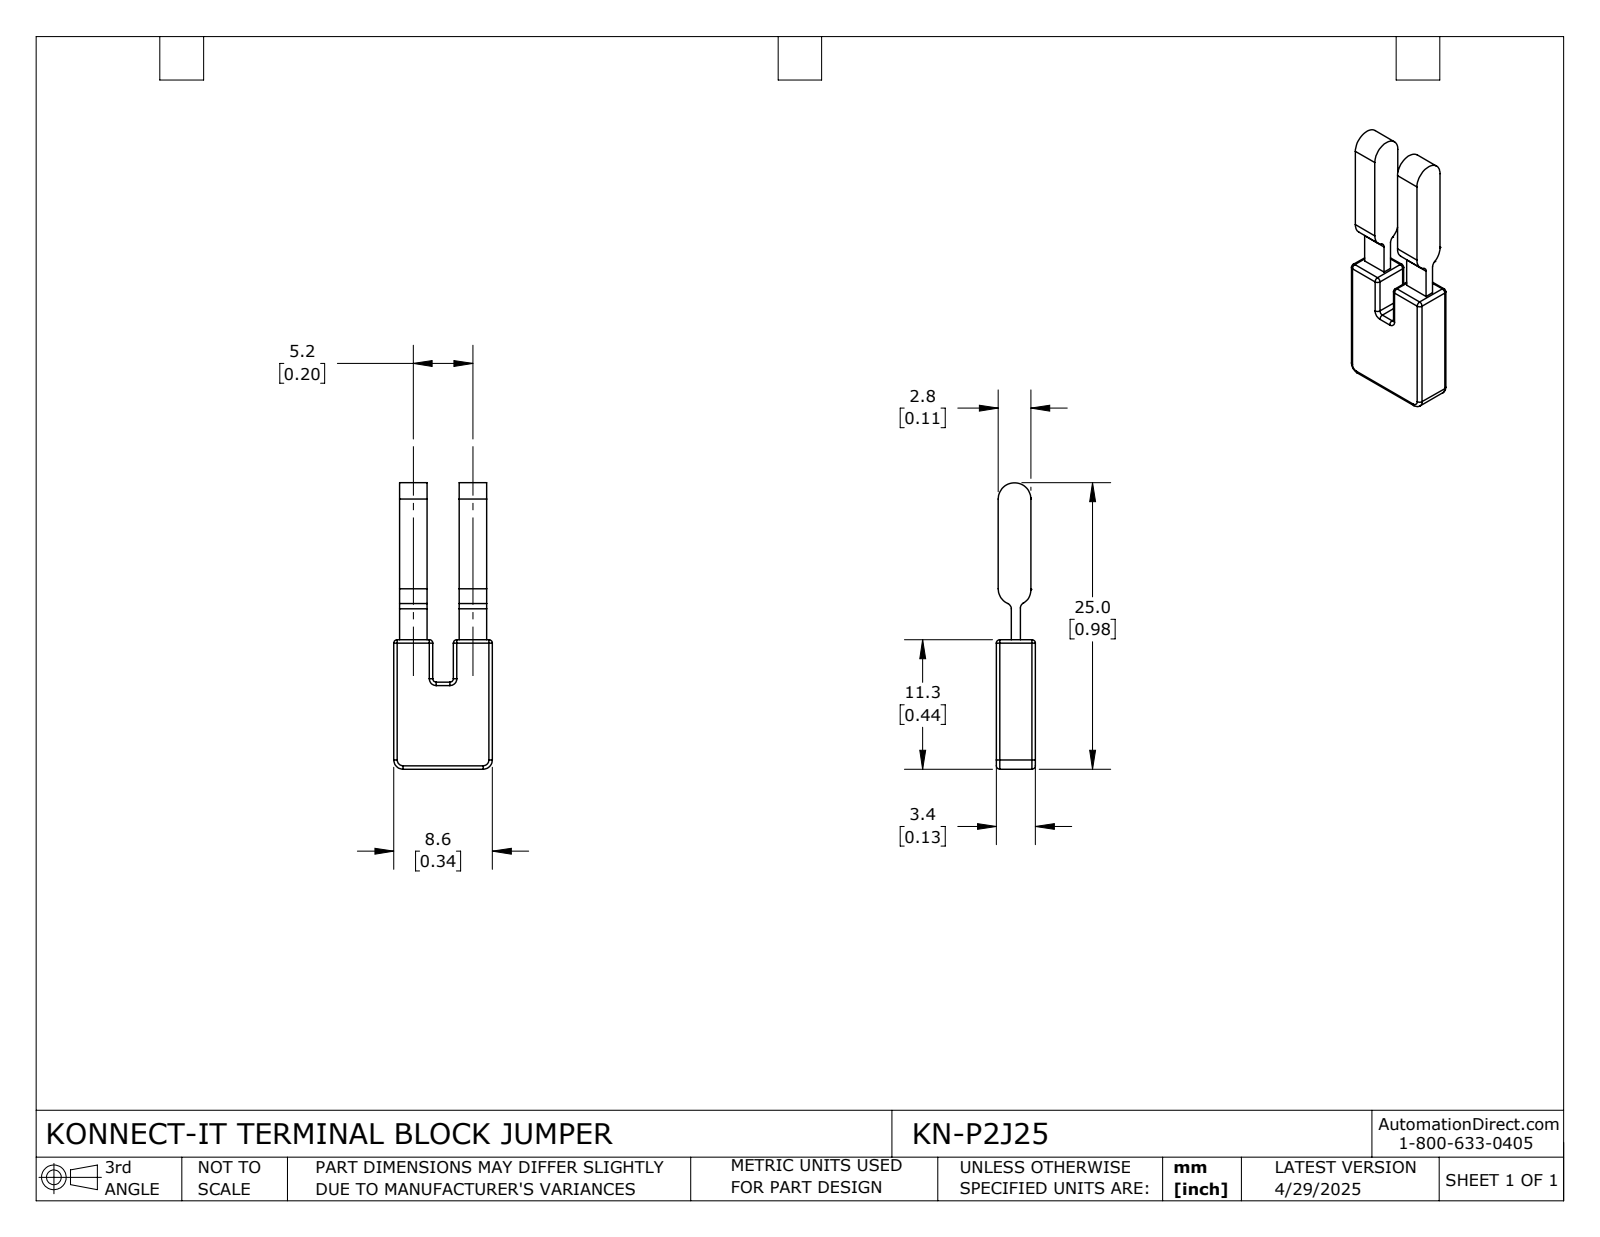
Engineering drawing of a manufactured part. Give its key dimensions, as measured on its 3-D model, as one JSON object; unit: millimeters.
{"part_name": "KN-P2J25", "step_written_by": "SolidWorks 2024 (CONFIG_CONTROL_DESIGN)", "units": "millimeters", "bodies": {"solids": 1, "faces": 81, "planar": 25, "cylindrical": 40, "other": 16}, "overall_size": [25, 8.6, 3.4], "volume_mm3": 455, "surface_area_mm2": 588, "partial_cylinders_radius": [[0.3, 20], [0.5, 2], [0.8, 2], [1, 2], [1.43, 2], [1.3, 1], [2, 1]], "face_to_face_distances": [3.4, 5.2, 0.5, 2.9, 2.4, 5.7, 8.1, 0.39, 3.01, 3.24]}
